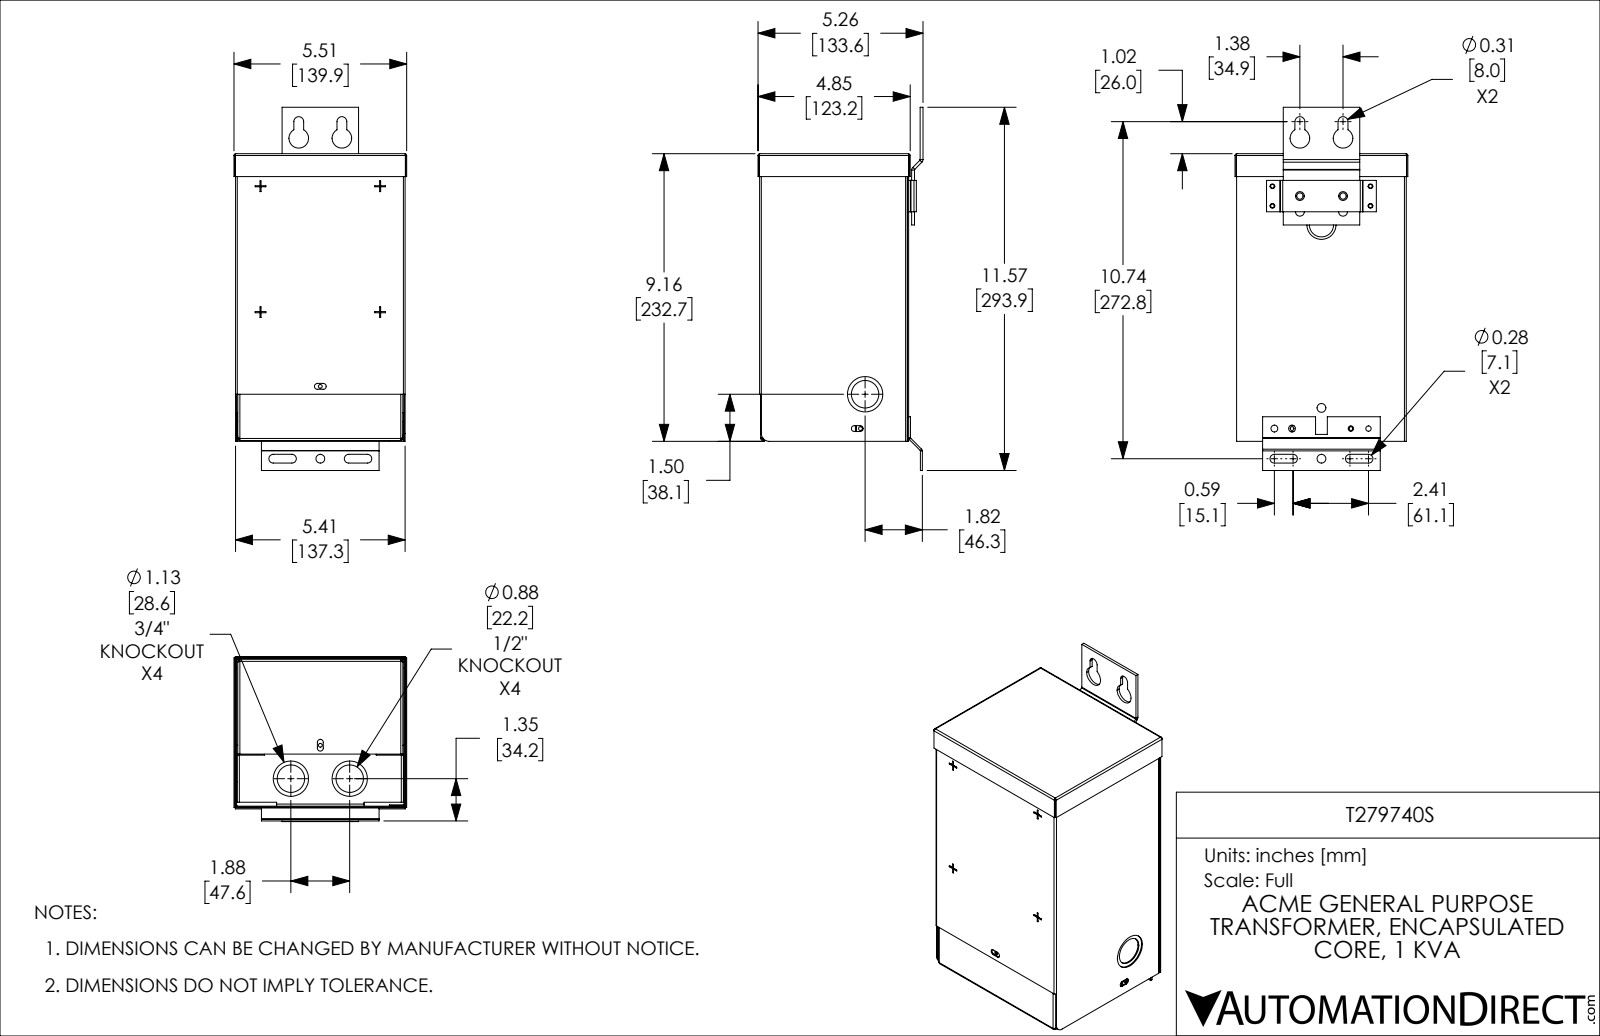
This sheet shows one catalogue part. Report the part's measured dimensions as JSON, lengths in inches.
{"part_name": "T279740S", "step_written_by": "SolidWorks 2021 (CONFIG_CONTROL_DESIGN)", "units": "inches", "bodies": {"solids": 7, "faces": 521, "planar": 329, "cylindrical": 152, "other": 40}, "overall_size": [11.57, 5.508, 5.259], "volume_in3": 10.83, "surface_area_in2": 570.5, "round_holes": [[0.281, 6], [0.12, 5], [0.875, 3], [1.125, 3], [0.172, 2], [0.187, 2], [0.201, 2], [0.219, 2], [0.625, 2]], "round_bosses_or_shafts": [[1.173, 1], [0.923, 1]], "partial_cylinders_radius": [[0.02, 10], [0.094, 10], [0.031, 8], [0.056, 8], [0.067, 8], [0.015, 4], [0.075, 4], [0.141, 4]], "face_to_face_distances": [0.036, 4.714, 5.37, 4.678, 5.335, 5.406, 4.75, 9.1, 0.051, 0.087], "hole_center_spacings": [1.375, 0.5, 0.563, 1.145, 1.342, 1.417, 1.463, 1.638]}
